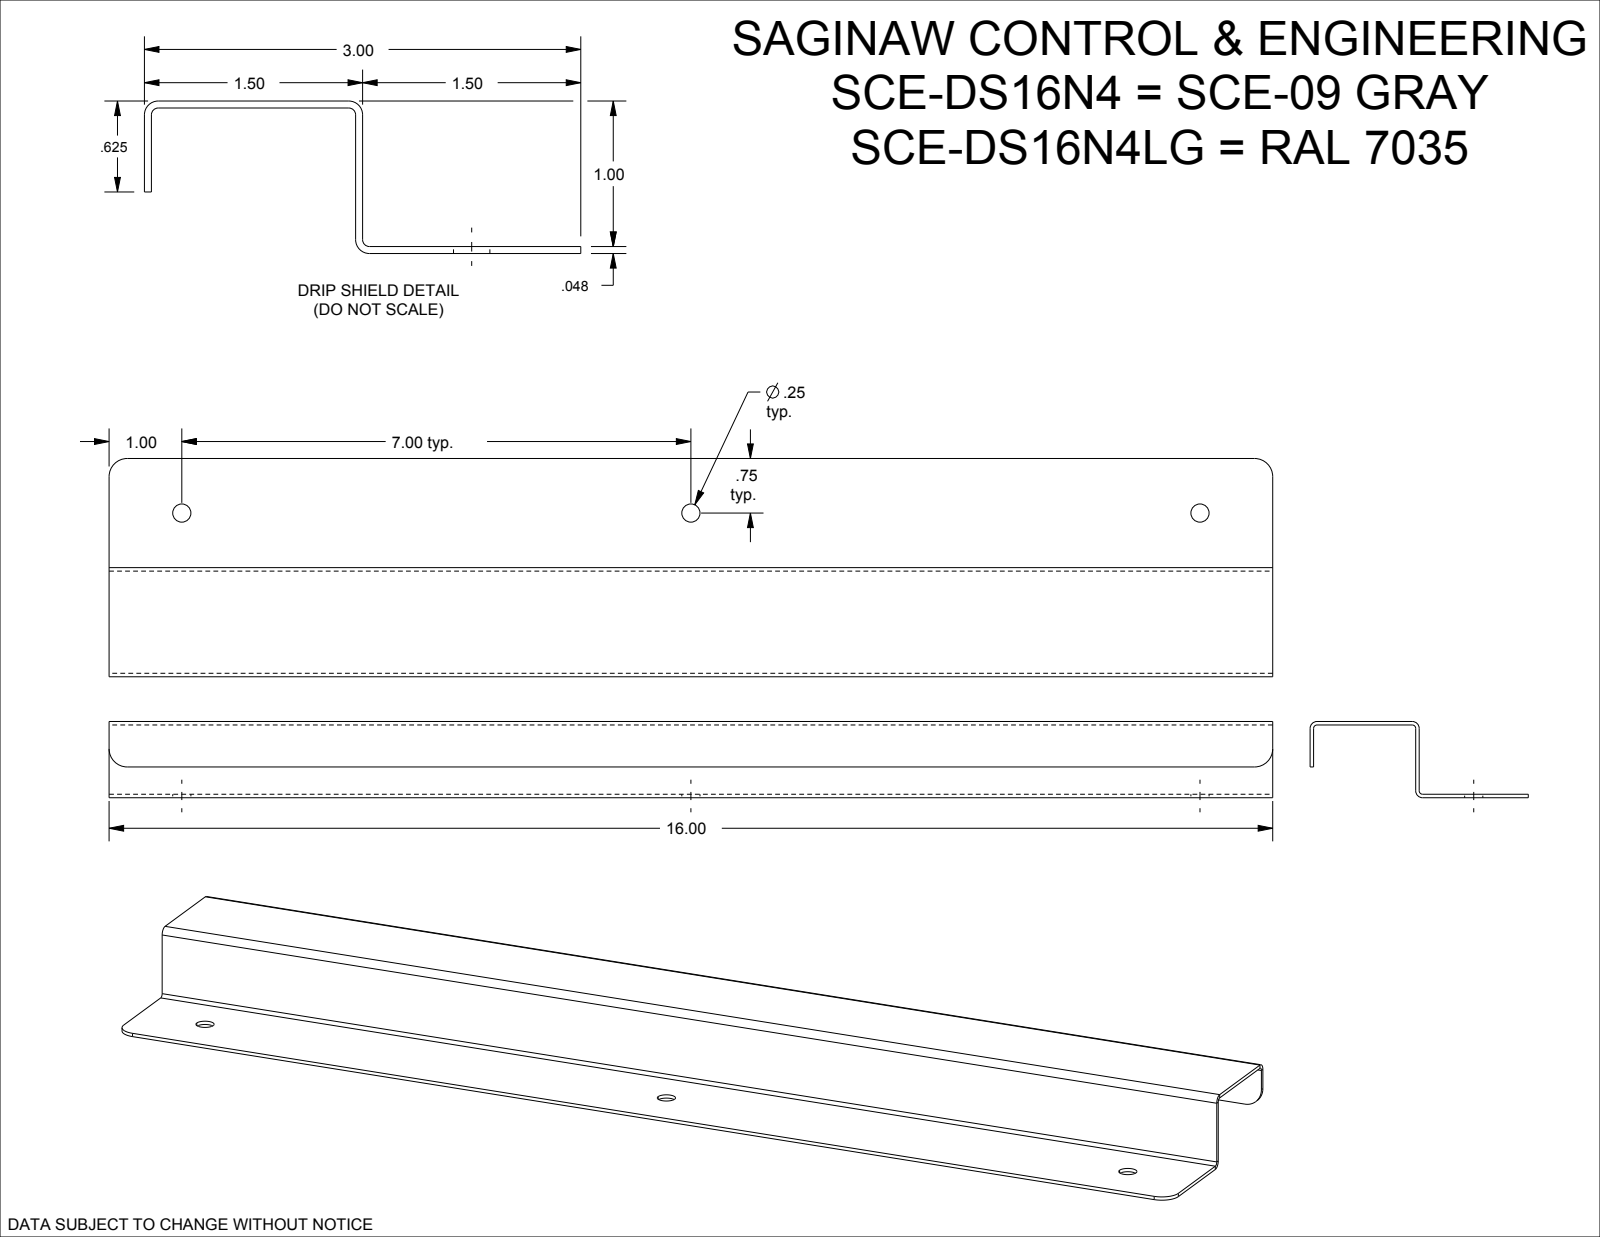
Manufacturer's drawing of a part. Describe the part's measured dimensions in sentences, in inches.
The part is named "SCE-DS16N4LG". Its 3-D file was written by "SolidWorks 2019 (CONFIG_CONTROL_DESIGN)". It is 1 solid with 25 faces: 12 planar, 13 cylindrical and 0 other. Overall it measures 16 by 3 by 1.048 inches. Its volume is 3.435 cubic inches and its surface area 145.2 square inches. Round holes: 3 of diameter 0.25. Partial cylindrical surfaces (rounded edges, fillets, slot ends): 4 of radius 0.25, 3 of radius 0.047, 3 of radius 0.095. The main face-to-face distances are 0.048, 1, 0.952, 1.048, 1.452, 1.5, 1.404, 0.423, 0.375, 0.577. The hole center spacings are 7, 14.
